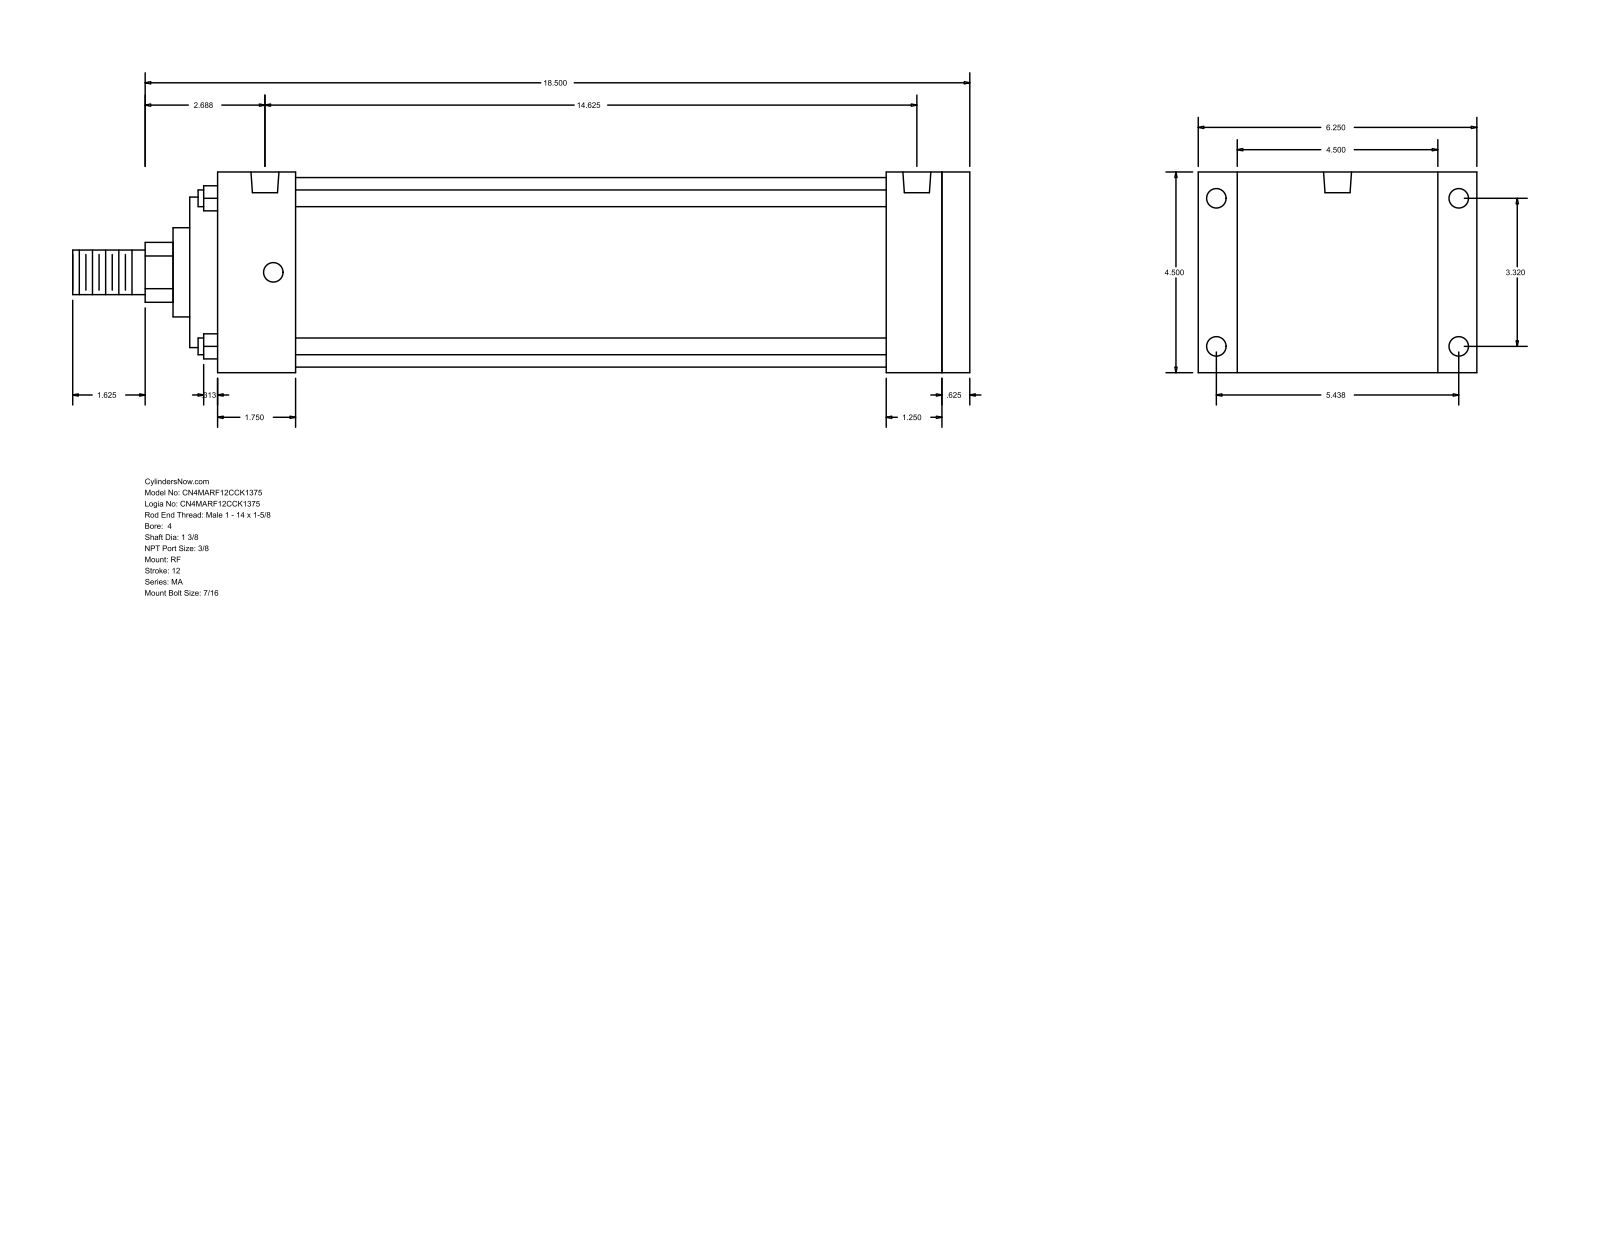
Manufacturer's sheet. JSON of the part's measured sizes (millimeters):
{"part_name": "MA_RF__0400_1.375", "step_written_by": "GSSL Pune (CONFIG_CONTROL_DESIGN)", "units": "millimeters", "bodies": {"solids": 0, "faces": 94, "planar": 65, "cylindrical": 29, "other": 0}, "overall_size": [511.18, 158.75, 114.3], "round_holes": [[11.11, 8], [15.93, 2]], "round_bosses_or_shafts": [[9.53, 4], [107.95, 1], [85.72, 1], [50.8, 1], [34.92, 1], [25.4, 1]], "partial_cylinders_radius": [[17.06, 1]], "face_to_face_distances": [114.3, 428.63, 15.88, 412.75, 15.87, 428.62, 444.5, 22.23, 136.53, 396.87], "hole_center_spacings": [84.32, 138.12, 161.82, 361.95, 4.76, 4.77, 366.71, 366.72]}
